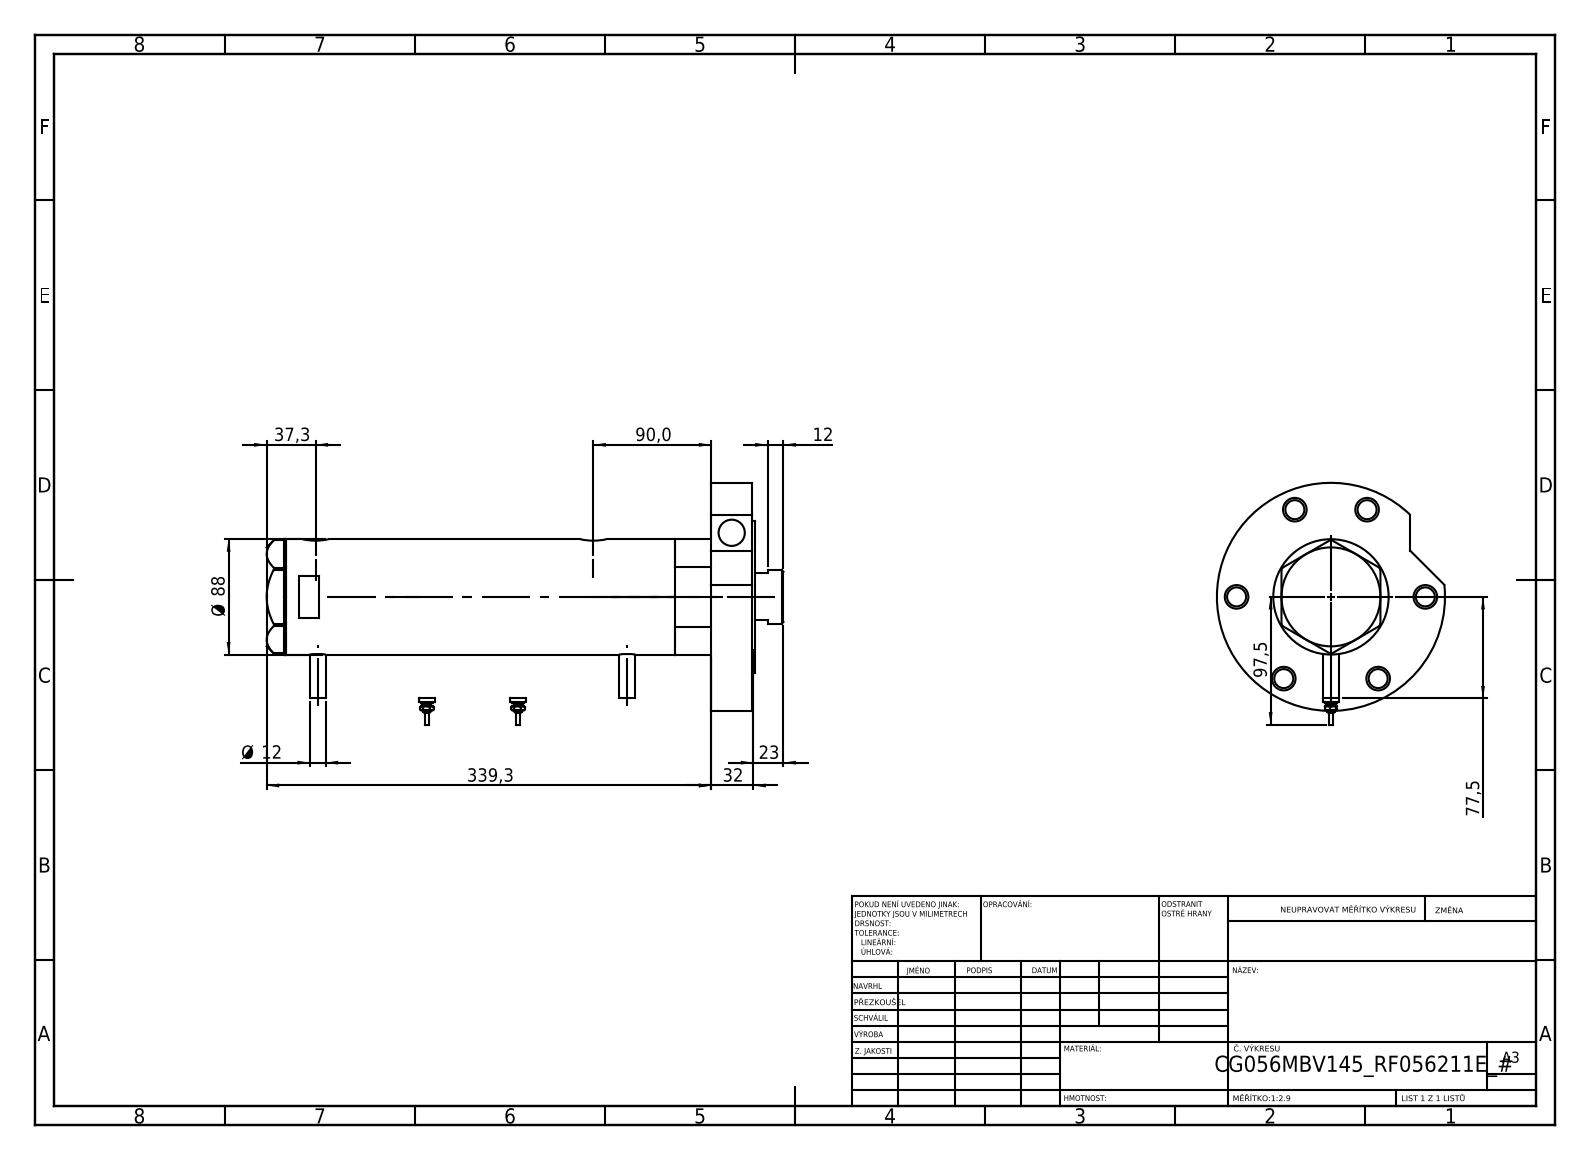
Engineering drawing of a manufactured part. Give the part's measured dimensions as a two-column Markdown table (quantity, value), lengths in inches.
| quantity | value |
| --- | --- |
| part name | V270CG_VC; V270CG_FRONT; Switch; V270CG_BACK (+2 more) |
| STEP written by | SolidWorks 2019 (CONFIG_CONTROL_DESIGN) |
| units | inches |
| bodies | 7 solids, 257 faces (91 planar, 102 cylindrical, 64 other) |
| overall size | 15.524 × 7.264 × 6.85 |
| volume | 156.6 in³ |
| surface area | 559.4 in² |
| round holes (diameter × count) | 0.571 × 7, 0.709 × 6, 0.787 × 3, 0.492 × 2, 0.518 × 2, 1.654 × 1, 1.713 × 1, 2.205 × 1, 2.362 × 1, 2.953 × 1, 3.15 × 1 |
| round bosses / shafts (diameter × count) | 0.472 × 4, 0.354 × 2, 0.276 × 2, 0.177 × 2, 0.098 × 2, 6.85 × 1, 4.567 × 1, 3.465 × 1 |
| main face-to-face distances | 1.22, 0.079, 14.067, 12.768, 13.988, 1.299, 9.228, 3.539, 4.76, 4.839 |
| hole center spacings | 2.835, 3.15, 4.714, 4.91, 5.085, 5.657, 0.067, 1.016 |
